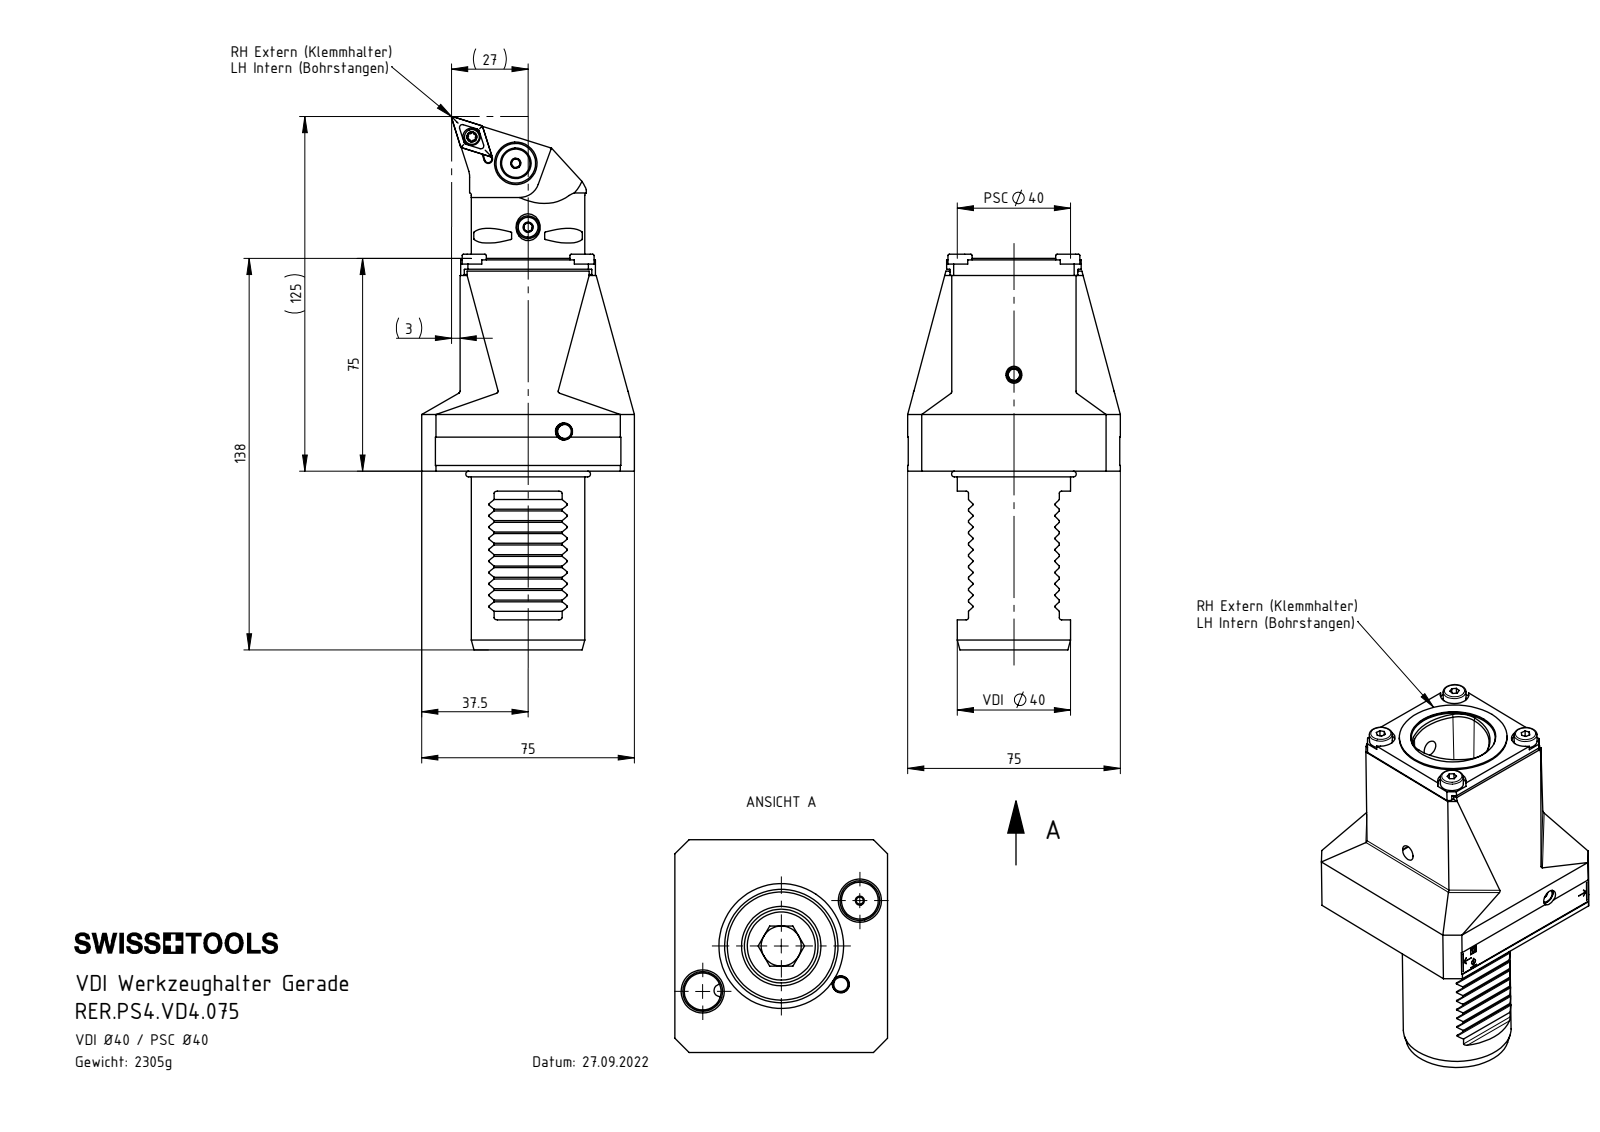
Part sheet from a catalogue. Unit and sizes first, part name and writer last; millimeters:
Units: millimetres
Overall size (bounding box): 139.5 × 75 × 75
Round holes (diameter × count): ⌀5 ×7, ⌀2.5 ×4, ⌀4.2 ×4, ⌀5.5 ×4, ⌀6 ×3, ⌀3 ×2, ⌀3.3 ×2, ⌀13 ×2, ⌀14 ×2, ⌀4 ×1, ⌀7 ×1, ⌀17 ×1
Round bosses / shafts (diameter × count): ⌀8.5 ×4, ⌀5 ×4, ⌀6 ×3, ⌀5.5 ×2, ⌀3 ×2, ⌀40 ×1, ⌀39.7 ×1, ⌀37.8 ×1
Partial cylindrical surfaces — rounded edges, fillets, slot ends (radius × count): R0.3 ×20, R0.8 ×9, R3.5 ×4, R5.25 ×4, R0.2 ×2, R2.75 ×2, R3 ×2, R9 ×1
Main face-to-face distances: 75, 3, 66, 24, 47.5, 2.83, 13.5, 69, 27, 14.14
Hole centre spacings: 20.25, 26.28, 26.87, 36.36, 38, 9.21, 12, 12.69
Volume: 312 726 mm³ · Surface area: 84 277 mm²
Bodies: 29 solids, 1004 faces (392 planar, 243 cylindrical, 369 other)
Part name (STEP PRODUCT): DIN 3771 - 11x1.5; U40-PS4.023.006_D; KVT_MB_600_060; VD4-ER1.014.010 (+8 more)
STEP written by: SolidWorks 2022 (AUTOMOTIVE_DESIGN)
